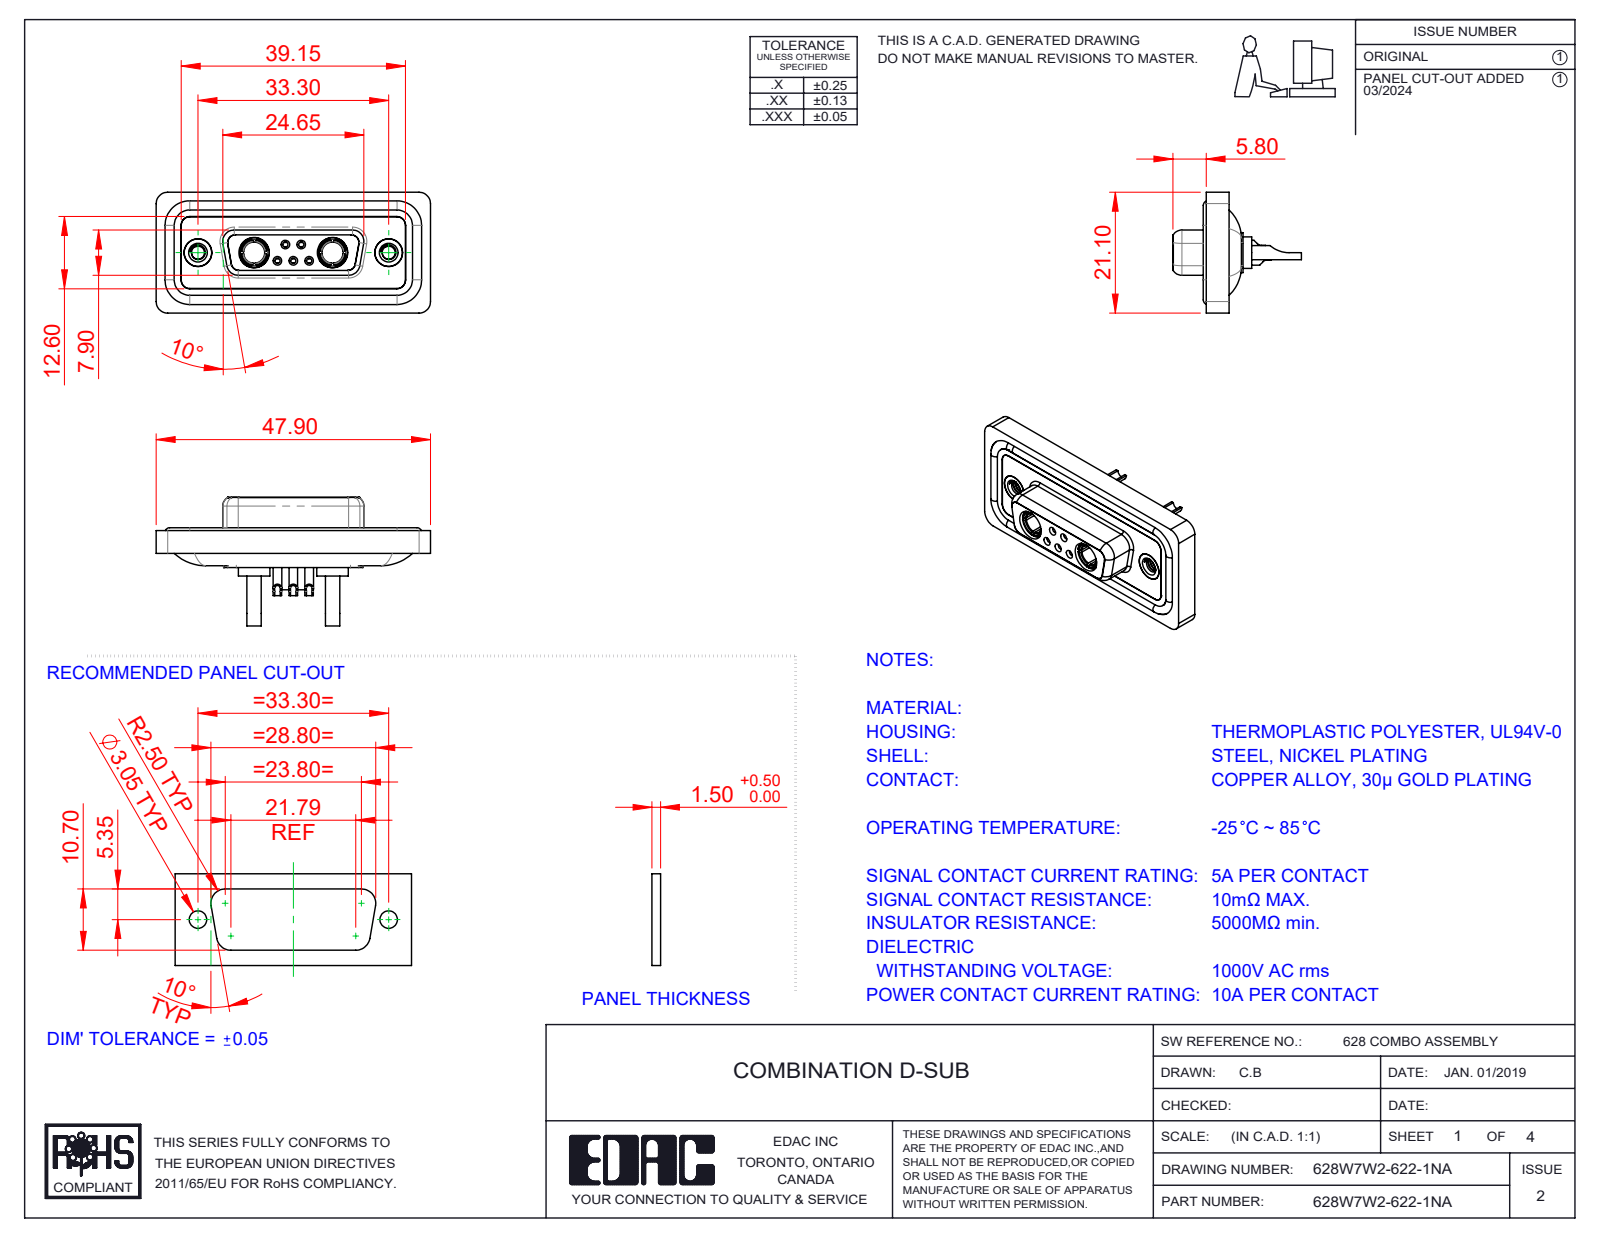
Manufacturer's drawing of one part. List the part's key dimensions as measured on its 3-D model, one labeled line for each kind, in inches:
Part name (STEP PRODUCT): 628Combo Waterproof Housing_15 Contacts; 628Combo Housing_7W2; Power Socket_10A SC; 628W7W2-622-1NA (+5 more)
STEP written by: SolidWorks 2023 (CONFIG_CONTROL_DESIGN)
Units: inches
Bodies: 16 solids, 817 faces (252 planar, 347 cylindrical, 218 other)
Overall size (bounding box): 1.886 × 0.884 × 0.831
Volume: 0.371 in³ · Surface area: 15.55 in²
Round holes (diameter × count): ⌀0.035 ×5, ⌀0.039 ×5, ⌀0.043 ×5, ⌀0.059 ×5, ⌀0.079 ×5, ⌀0.191 ×4, ⌀0.063 ×3, ⌀0.067 ×2, ⌀0.067 ×2, ⌀0.089 ×2, ⌀0.146 ×2, ⌀0.157 ×2
Round bosses / shafts (diameter × count): ⌀0.063 ×6, ⌀0.087 ×5, ⌀0.217 ×2, ⌀0.205 ×2, ⌀0.195 ×2, ⌀0.195 ×2, ⌀0.189 ×2, ⌀0.187 ×2
Partial cylindrical surfaces — rounded edges, fillets, slot ends (radius × count): R0.059 ×22, R0.079 ×20, R0.053 ×12, R0.063 ×8, R0.039 ×6, R0.01 ×4, R0.02 ×4, R0.024 ×4
Main face-to-face distances: 0.016, 0.071, 0.063, 0.02, 0.114, 0.043, 0.293, 0.222, 0.26, 0.278
Hole centre spacings: 0.124, 0.109, 0.386, 0.925, 0.17, 0.17, 0.198, 0.198
